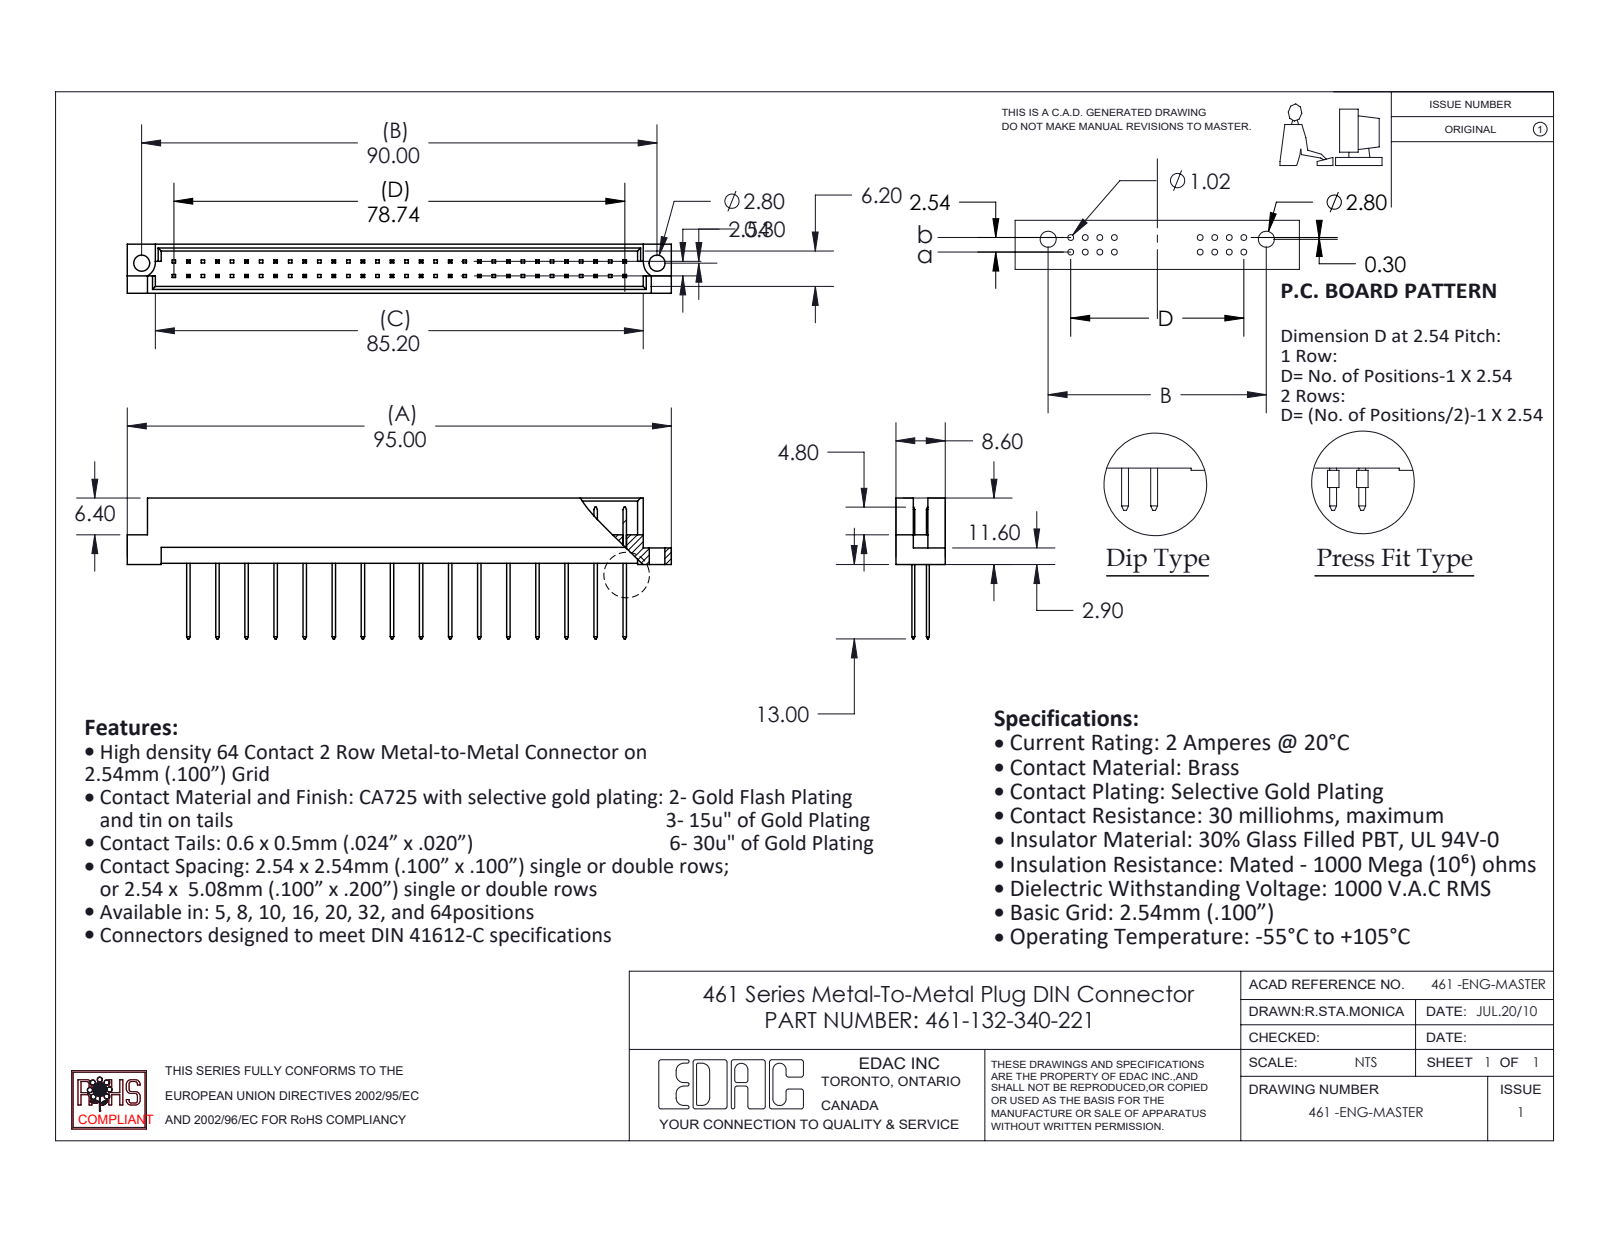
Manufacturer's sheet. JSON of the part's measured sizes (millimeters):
{"part_name": "461 Part_64; 461-290_40; 461-132-340-221", "step_written_by": "SolidWorks 2020 (CONFIG_CONTROL_DESIGN)", "units": "millimeters", "bodies": {"solids": 33, "faces": 753, "planar": 746, "cylindrical": 7, "other": 0}, "overall_size": [95, 24.6, 8.6], "volume_mm3": 4874, "surface_area_mm2": 7278, "round_holes": [[2.8, 2]], "partial_cylinders_radius": [[2.8, 2]], "face_to_face_distances": [1.2, 7.4, 8.6, 6.2, 2.54, 3.28, 5.32, 2.08, 4.12, 2.78], "hole_center_spacings": [90]}
